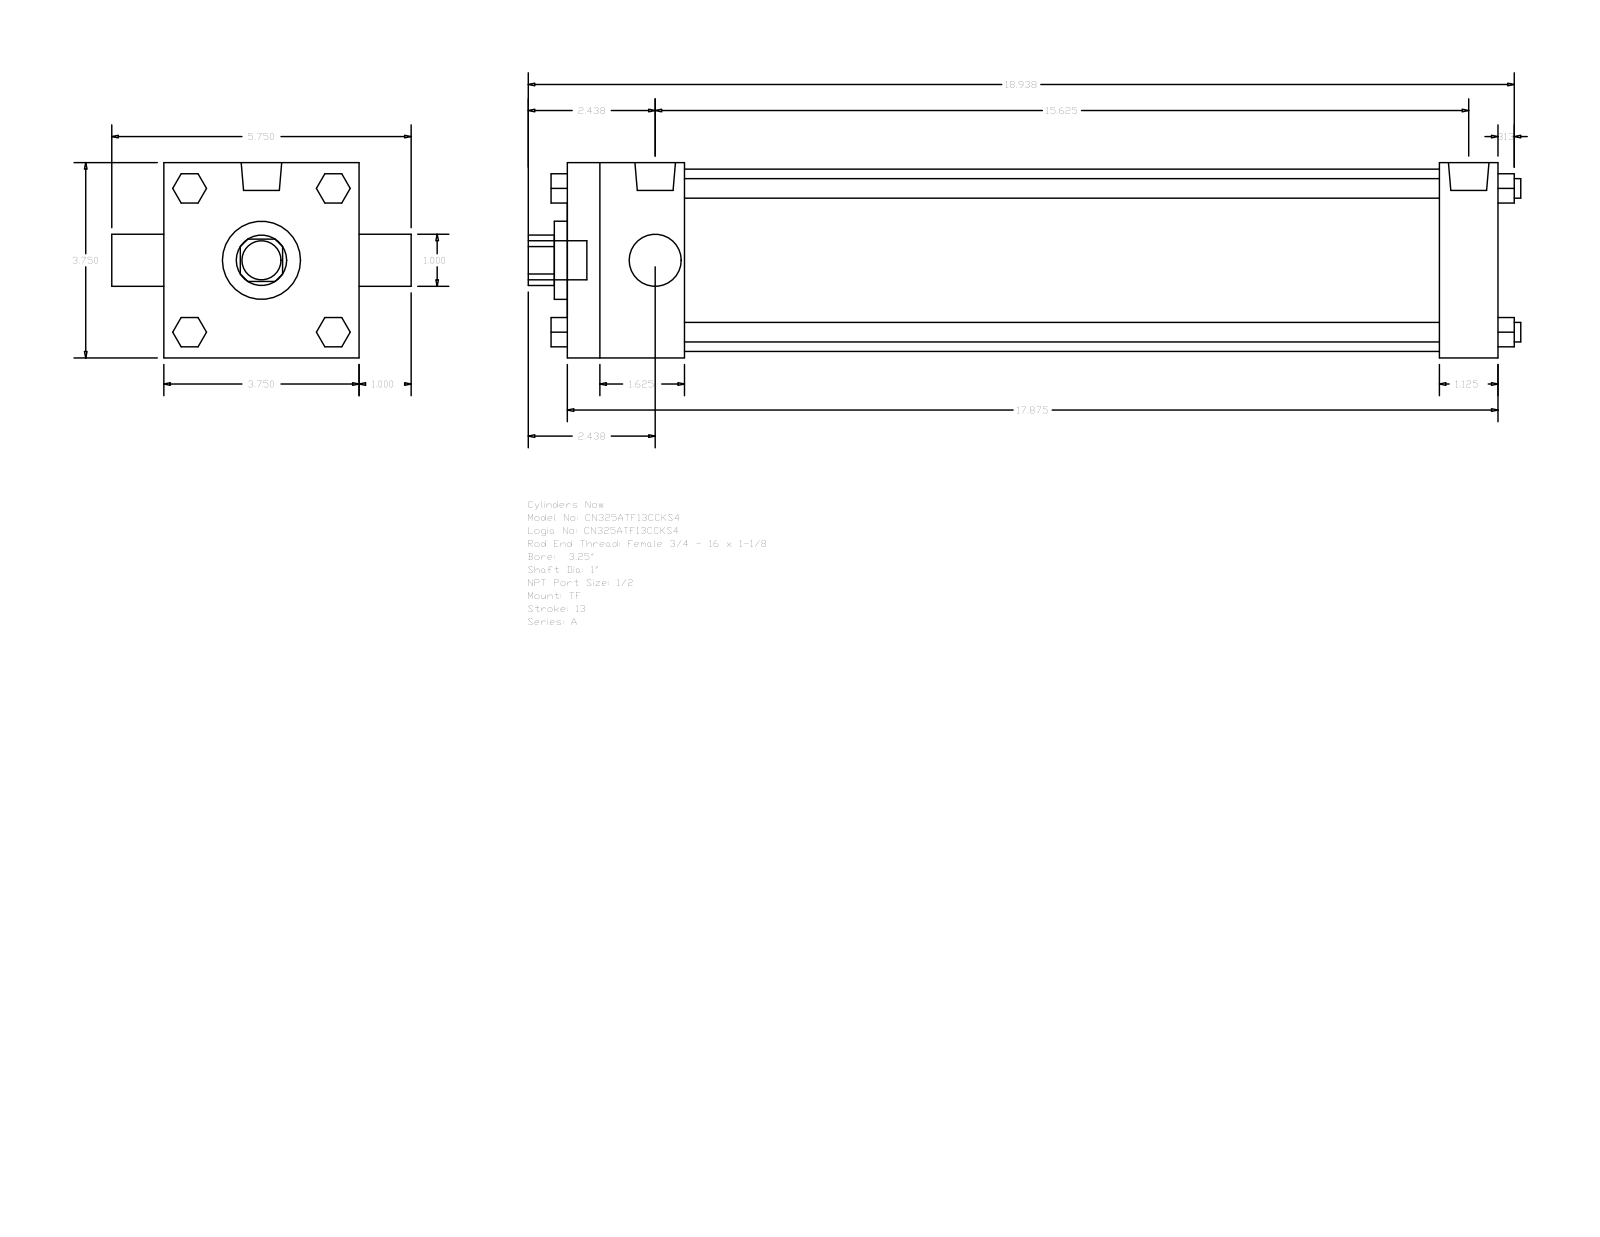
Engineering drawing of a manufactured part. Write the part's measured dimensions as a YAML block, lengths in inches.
part_name: "A_TF__0325_1"
step_written_by: "GSSL Pune (CONFIG_CONTROL_DESIGN)"
units: inches
bodies: {solids: 0, faces: 120, planar: 92, cylindrical: 28, other: 0}
overall_size: [19.063, 5.75, 3.75]
round_holes:
  - {diameter: 1, count: 2}
  - {diameter: 1.5, count: 1}
  - {diameter: 3.5, count: 1}
round_bosses_or_shafts:
  - {diameter: 0.375, count: 4}
  - {diameter: 0.344, count: 3}
  - {diameter: 0.778, count: 2}
  - {diameter: 0.75, count: 1}
partial_cylinders:
  - {radius: 0.484, count: 1}
face_to_face_distances: [3.75, 17.875, 1.125, 2.25, 16.75, 14.5, 15.625, 0.562, 1.38, 2.39]
